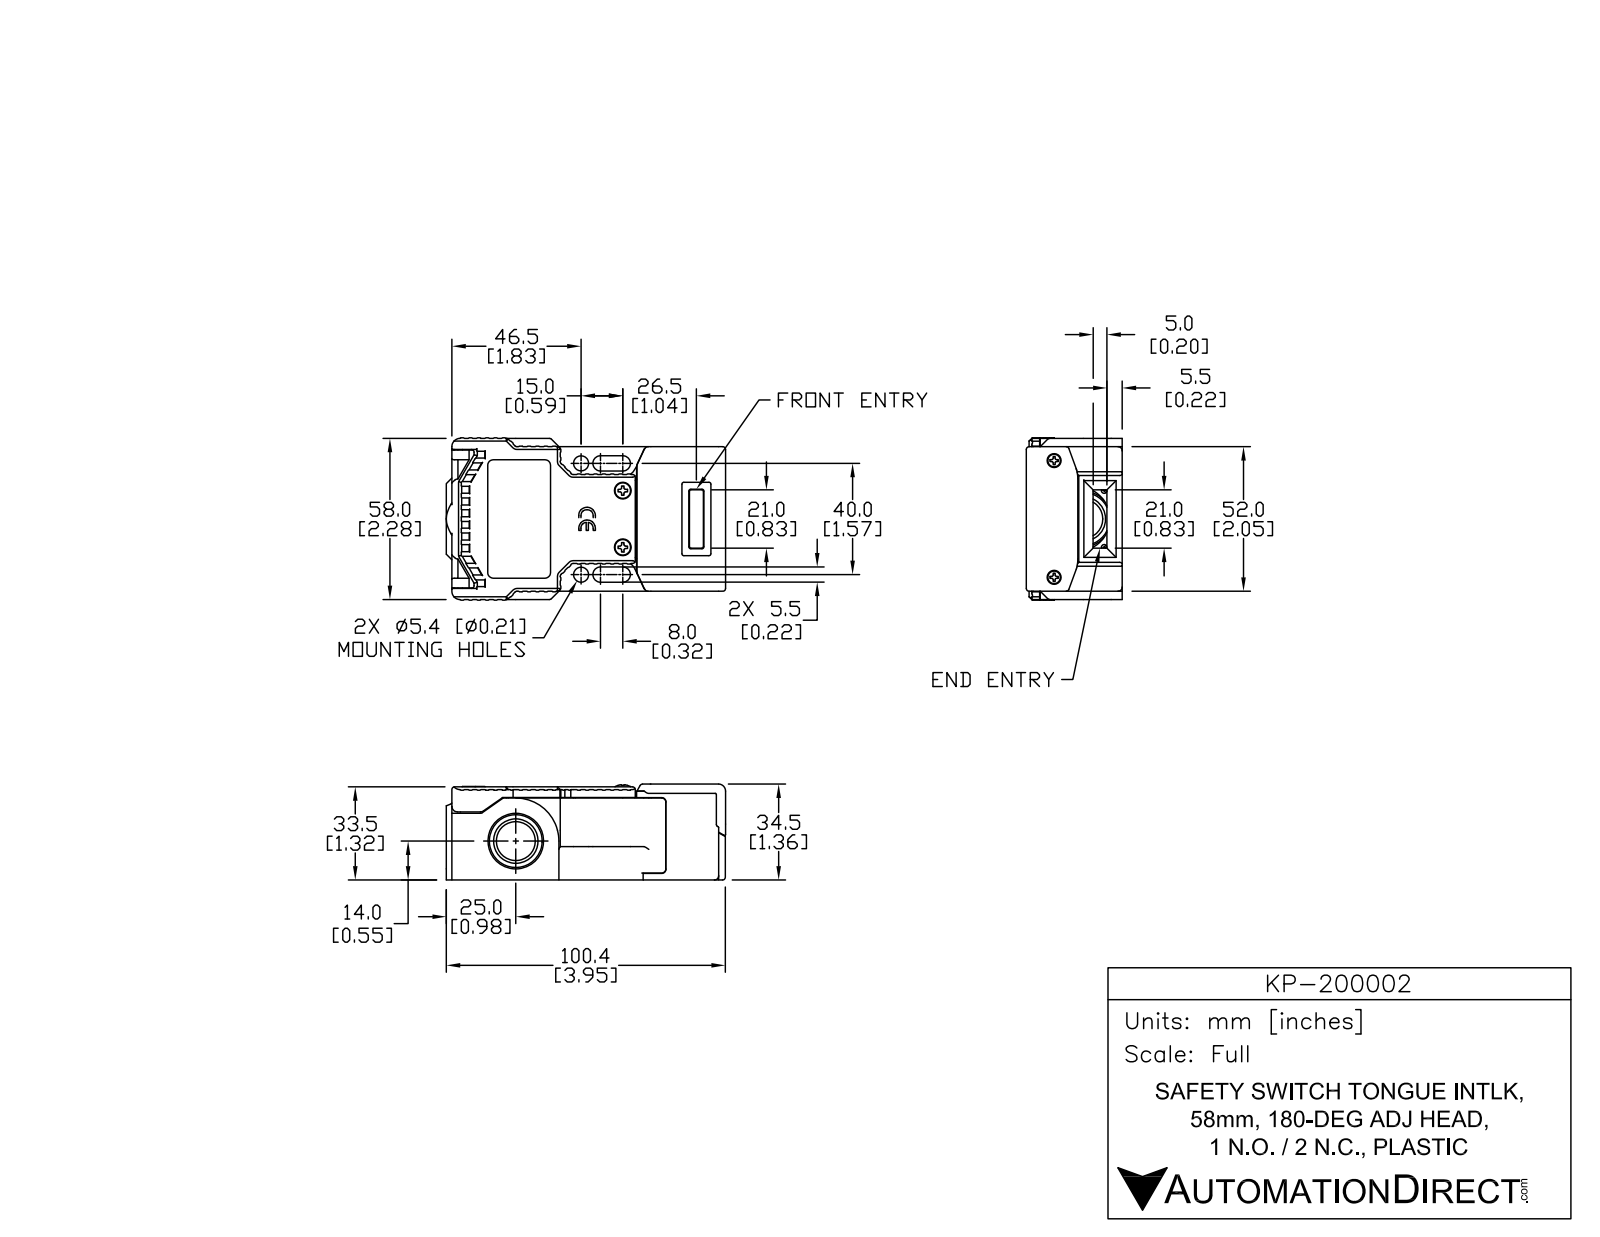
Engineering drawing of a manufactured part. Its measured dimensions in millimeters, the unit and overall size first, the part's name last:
Units: millimetres
Overall size (bounding box): 101.85 × 58 × 34.6
Round holes (diameter × count): ⌀5.4 ×2, ⌀19.33 ×1, ⌀20 ×1
Round bosses / shafts (diameter × count): ⌀5.6 ×2, ⌀4.5 ×2
Partial cylindrical surfaces — rounded edges, fillets, slot ends (radius × count): R2 ×4, R2.75 ×4, R4 ×3, R5 ×2
Main face-to-face distances: 33.5, 52, 3, 55, 34.5, 1, 33.45, 1.05, 12.8, 98.5
Hole centre spacings: 40
Volume: 158 770 mm³ · Surface area: 25 501 mm²
Bodies: 1 solid, 206 faces (147 planar, 32 cylindrical, 27 other)
Part name (STEP PRODUCT): KP-200002
STEP written by: SolidWorks 2013 (AUTOMOTIVE_DESIGN)
